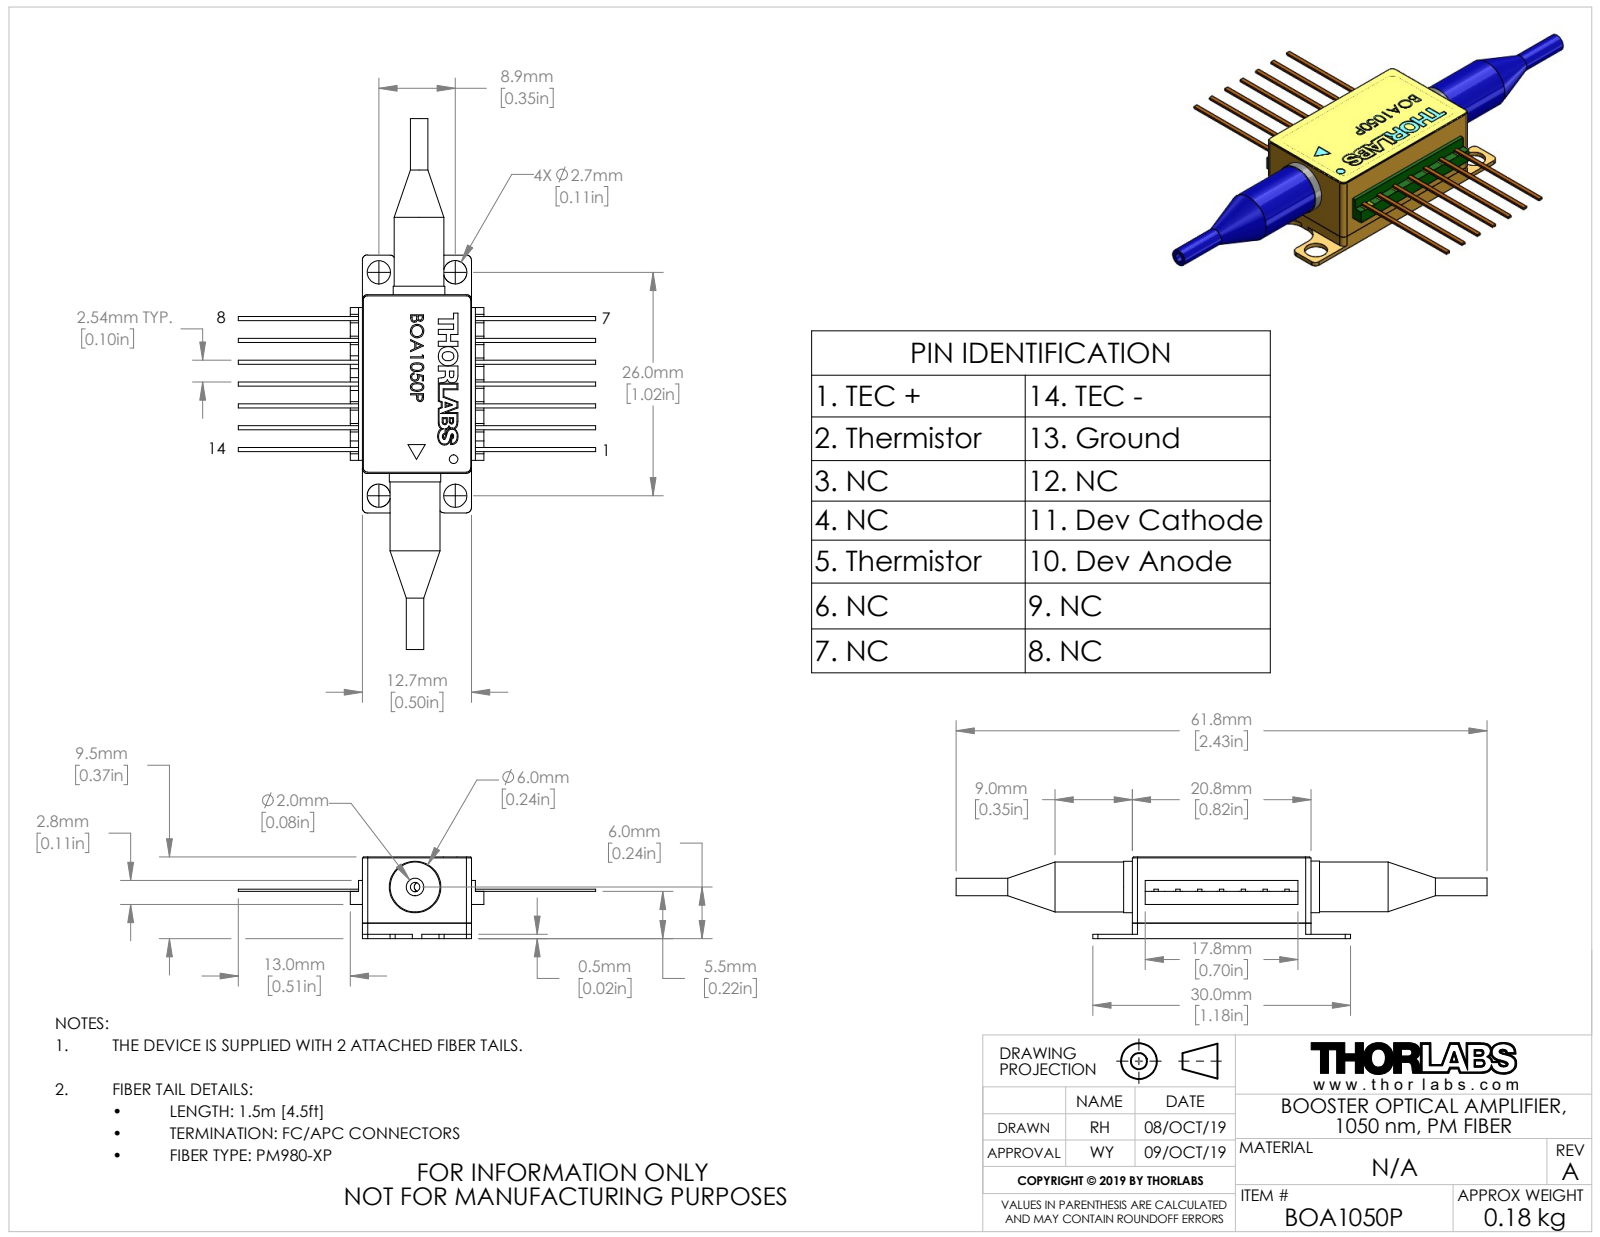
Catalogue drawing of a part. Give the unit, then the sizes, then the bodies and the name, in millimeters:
Units: millimetres
Overall size (bounding box): 61.8 × 41.6 × 9.5
Round holes (diameter × count): ⌀2.7 ×4, ⌀1.1 ×2, ⌀1 ×1
Round bosses / shafts (diameter × count): ⌀6 ×2, ⌀5.8 ×2, ⌀2.04 ×2
Partial cylindrical surfaces — rounded edges, fillets, slot ends (radius × count): R0.6 ×12, R0.5 ×4, R2 ×4
Main face-to-face distances: 9.5, 12.7, 1.8, 7.7, 3.7, 2.17, 3.97, 5.53, 3.95, 1.53
Hole centre spacings: 8.9, 26, 27.48, 0.47, 4.26, 9.69, 21.74, 23.42
Bodies: 0 solids, 396 faces (265 planar, 50 cylindrical, 81 other)
Part name (STEP PRODUCT): QTN037706-E0W
STEP written by: SolidWorks 2018 (AUTOMOTIVE_DESIGN)
